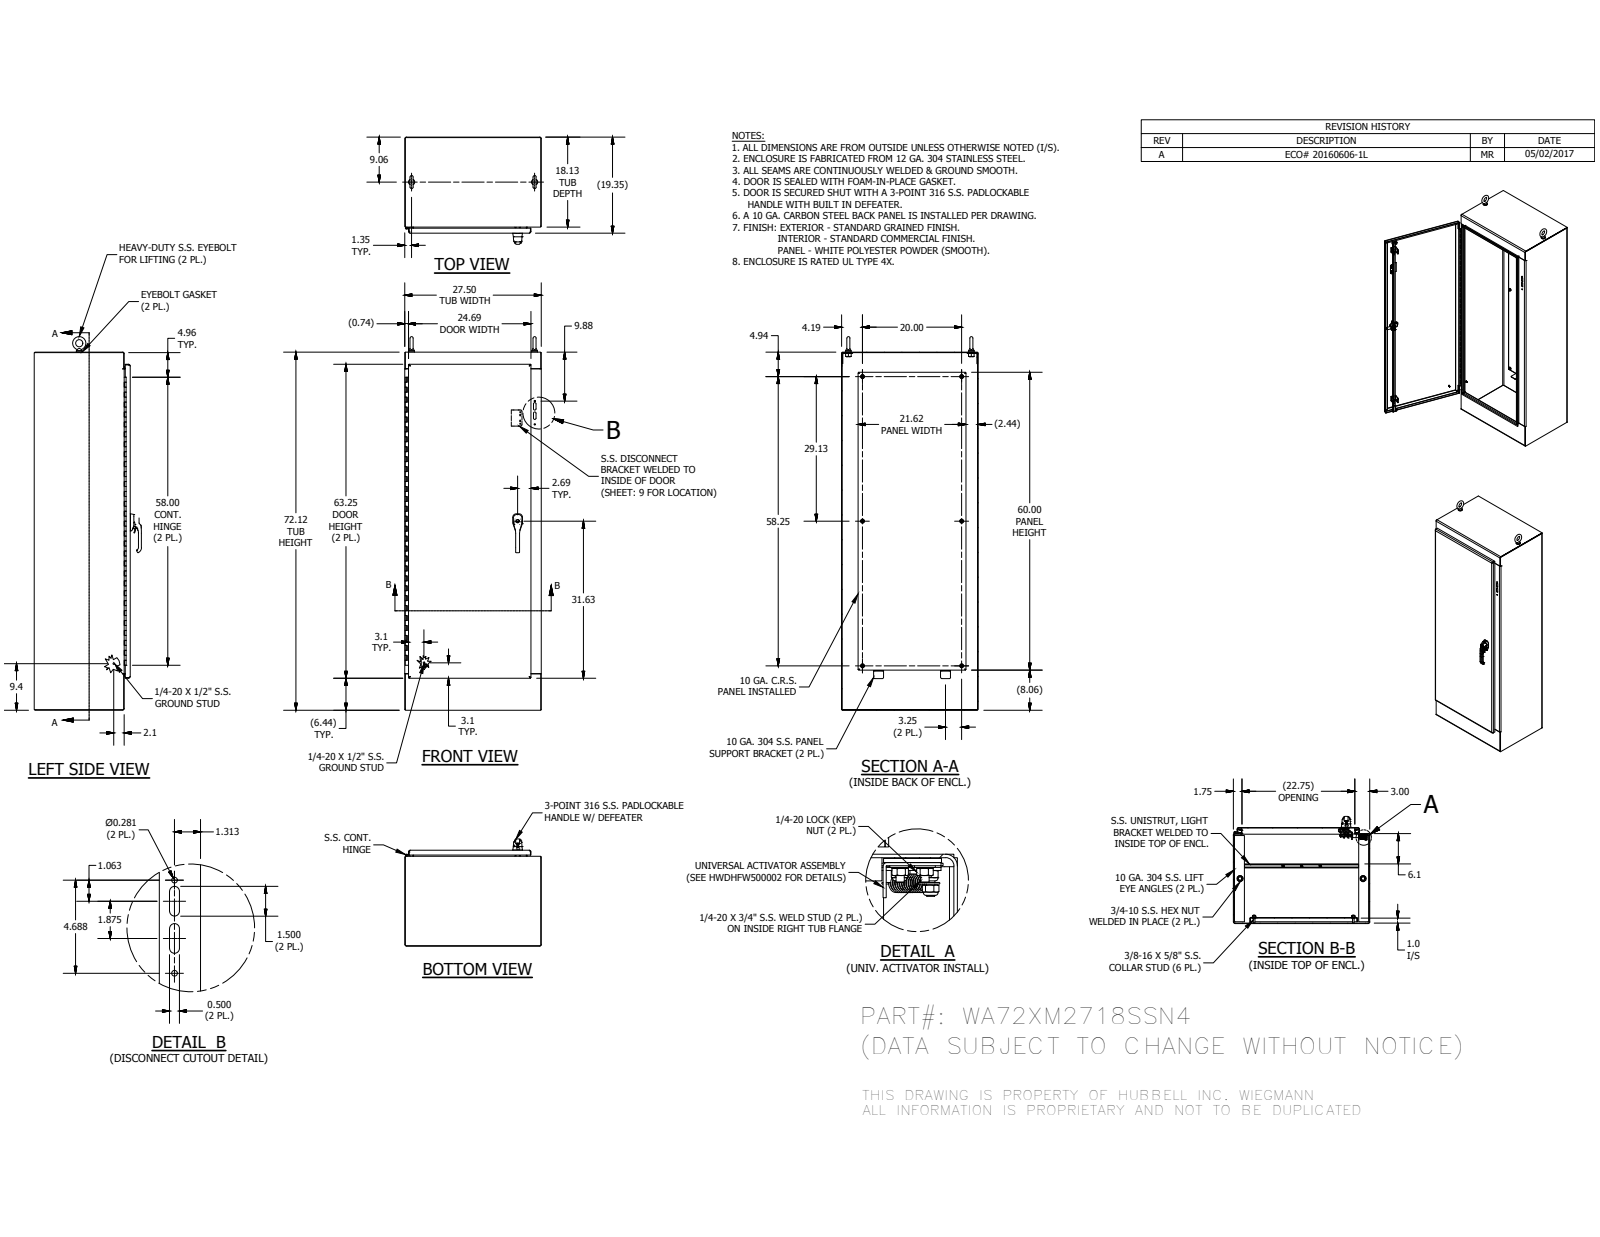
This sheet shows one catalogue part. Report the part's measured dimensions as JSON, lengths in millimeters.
{"part_name": "WA72XM2718SSN4BLR; WAXM2718SSN4TOP; WAXM2718SSN4BTM; FUN00129_WAXM27SSN4 (+8 more)", "step_written_by": "Autodesk Inventor 2016 (AUTOMOTIVE_DESIGN)", "units": "millimeters", "bodies": {"solids": 126, "faces": 4763, "planar": 2197, "cylindrical": 1524, "other": 1042}, "overall_size": [1911.29, 698.5, 548.55], "volume_mm3": 18630000, "surface_area_mm2": 13280000, "round_holes": [[3.55, 24], [9.52, 10], [6.35, 9], [6.65, 8], [3.96, 6], [7.8, 6], [14.29, 6], [4.76, 5], [3.45, 4], [4.17, 4], [5.1, 4], [7.37, 4]], "round_bosses_or_shafts": [[15.88, 10], [8.38, 9], [14.29, 6], [13.54, 4], [8.56, 4], [6.35, 4], [6.02, 4], [6, 3]], "partial_cylinders_radius": [[0.5, 187], [0.3, 109], [0.51, 48], [6.35, 26], [0.47, 21], [1.59, 20], [3.17, 18], [0.64, 16]], "face_to_face_distances": [2.64, 488.79, 695.86, 486.15, 491.43, 3.41, 25.4, 693.22, 463.39, 31.45], "hole_center_spacings": [0.45, 163.69, 1379.46, 0.59, 0.6, 0.74, 9.65, 19.31]}
